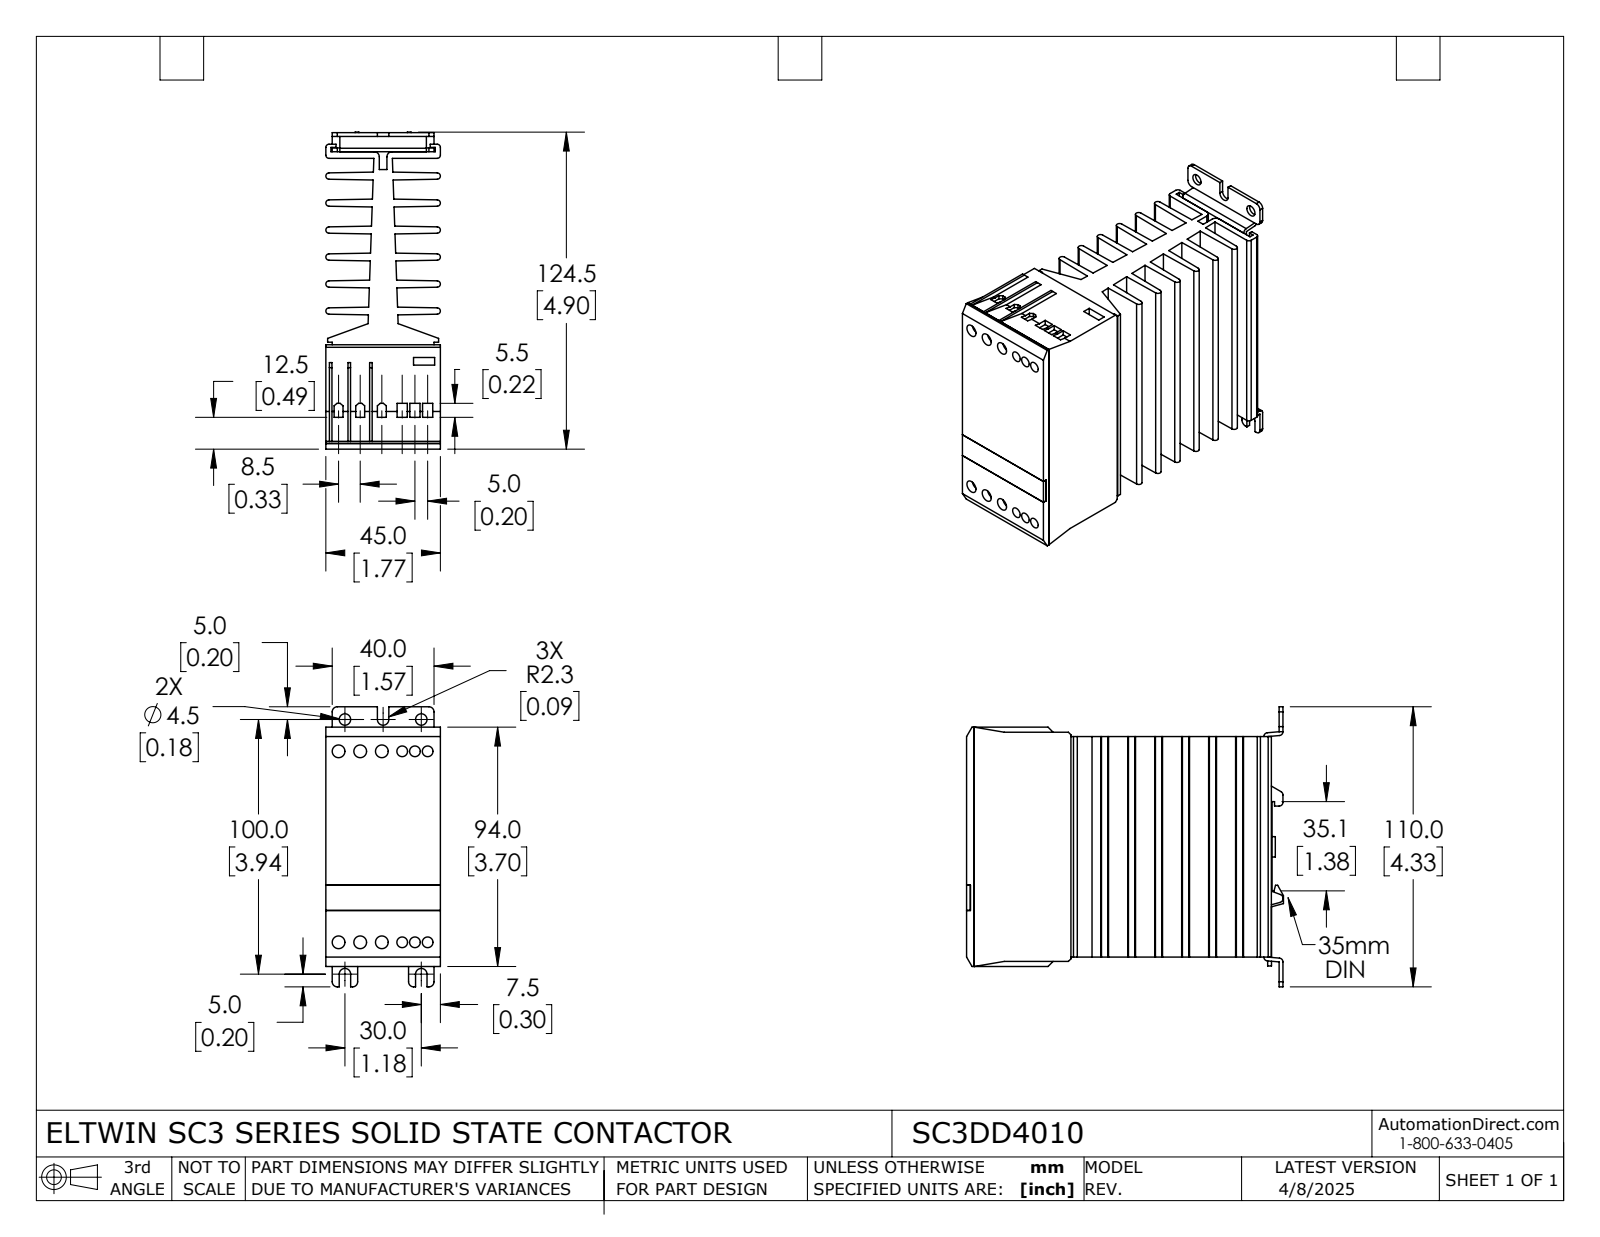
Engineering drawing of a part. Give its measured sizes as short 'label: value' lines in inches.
name: SC3DD4010
written by: SolidWorks 2021 (AUTOMOTIVE_DESIGN)
unit: in
bodies: 5 solids, 427 faces (316 planar, 111 cylindrical, 0 other)
size: 4.902 × 4.331 × 1.772
volume: 18.87 in³; area: 165.9 in²
holes: 6× ⌀0.165, 6× ⌀0.173, 6× ⌀0.197, 6× ⌀0.236, 2× ⌀0.177
bosses: 1× ⌀0.315
rounds: 18× R0.079, 16× R0.049, 10× R0.059, 4× R0.051, 3× R0.089
face distances: 0.417, 0.835, 0.127, 1.252, 0.29, 0.544, 0.707, 0.962, 1.669, 1.125
hole spacings: 2.953, 0.197, 0.335, 2.959, 2.972, 0.502, 1.181, 3.446
